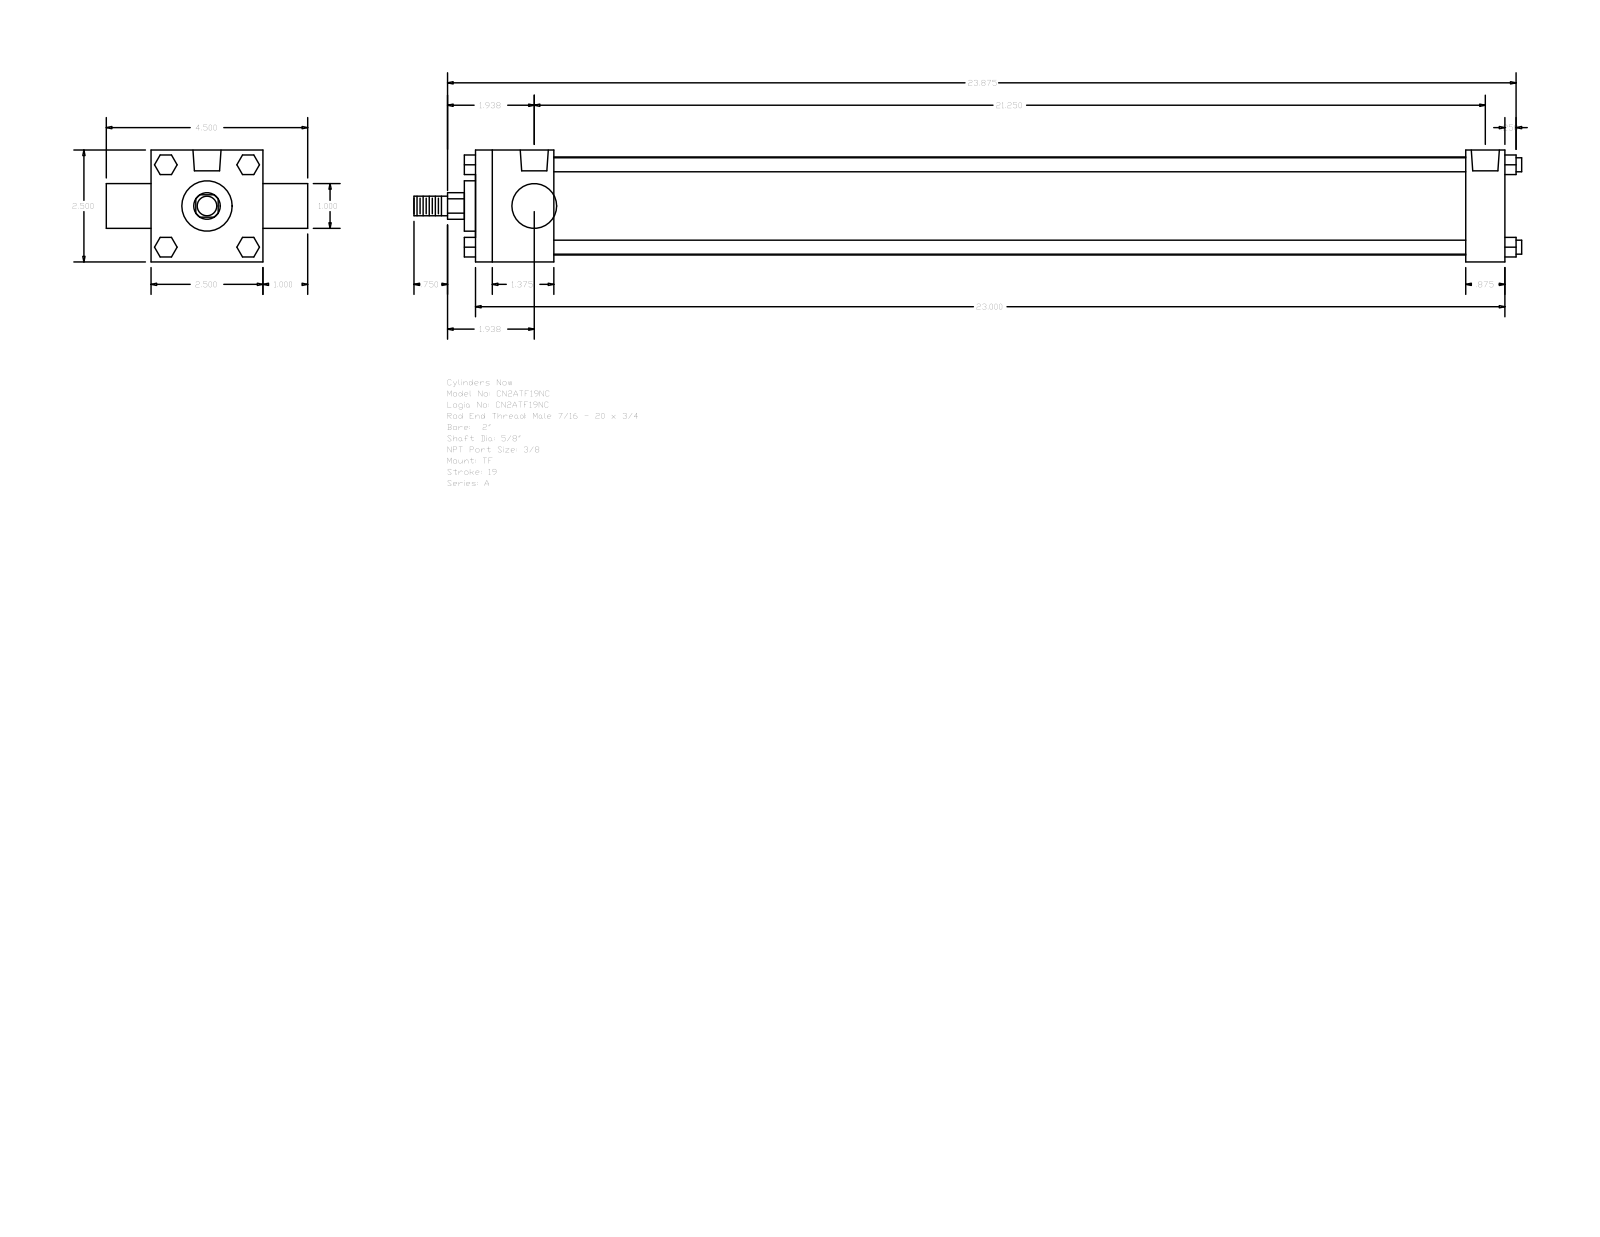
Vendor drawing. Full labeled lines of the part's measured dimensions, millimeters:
Part name (STEP PRODUCT): A_TF__0200_0.625
STEP written by: GSSL Pune (CONFIG_CONTROL_DESIGN)
Units: millimetres
Bodies: 0 solids, 120 faces (92 planar, 28 cylindrical, 0 other)
Overall size (bounding box): 628.65 × 114.3 × 63.5
Round holes (diameter × count): ⌀5.56 ×3, ⌀15.93 ×2
Round bosses / shafts (diameter × count): ⌀7.94 ×4, ⌀55.63 ×1, ⌀28.57 ×1, ⌀25.4 ×1, ⌀15.88 ×1, ⌀11.11 ×1
Partial cylindrical surfaces — rounded edges, fillets, slot ends (radius × count): R7.54 ×1
Main face-to-face distances: 63.5, 584.2, 44.45, 561.97, 517.52, 539.75, 22.23, 25.4, 88.9, 50.8
Hole centre spacings: 3.97, 3.98, 531.8, 535.77, 535.78, 539.75
